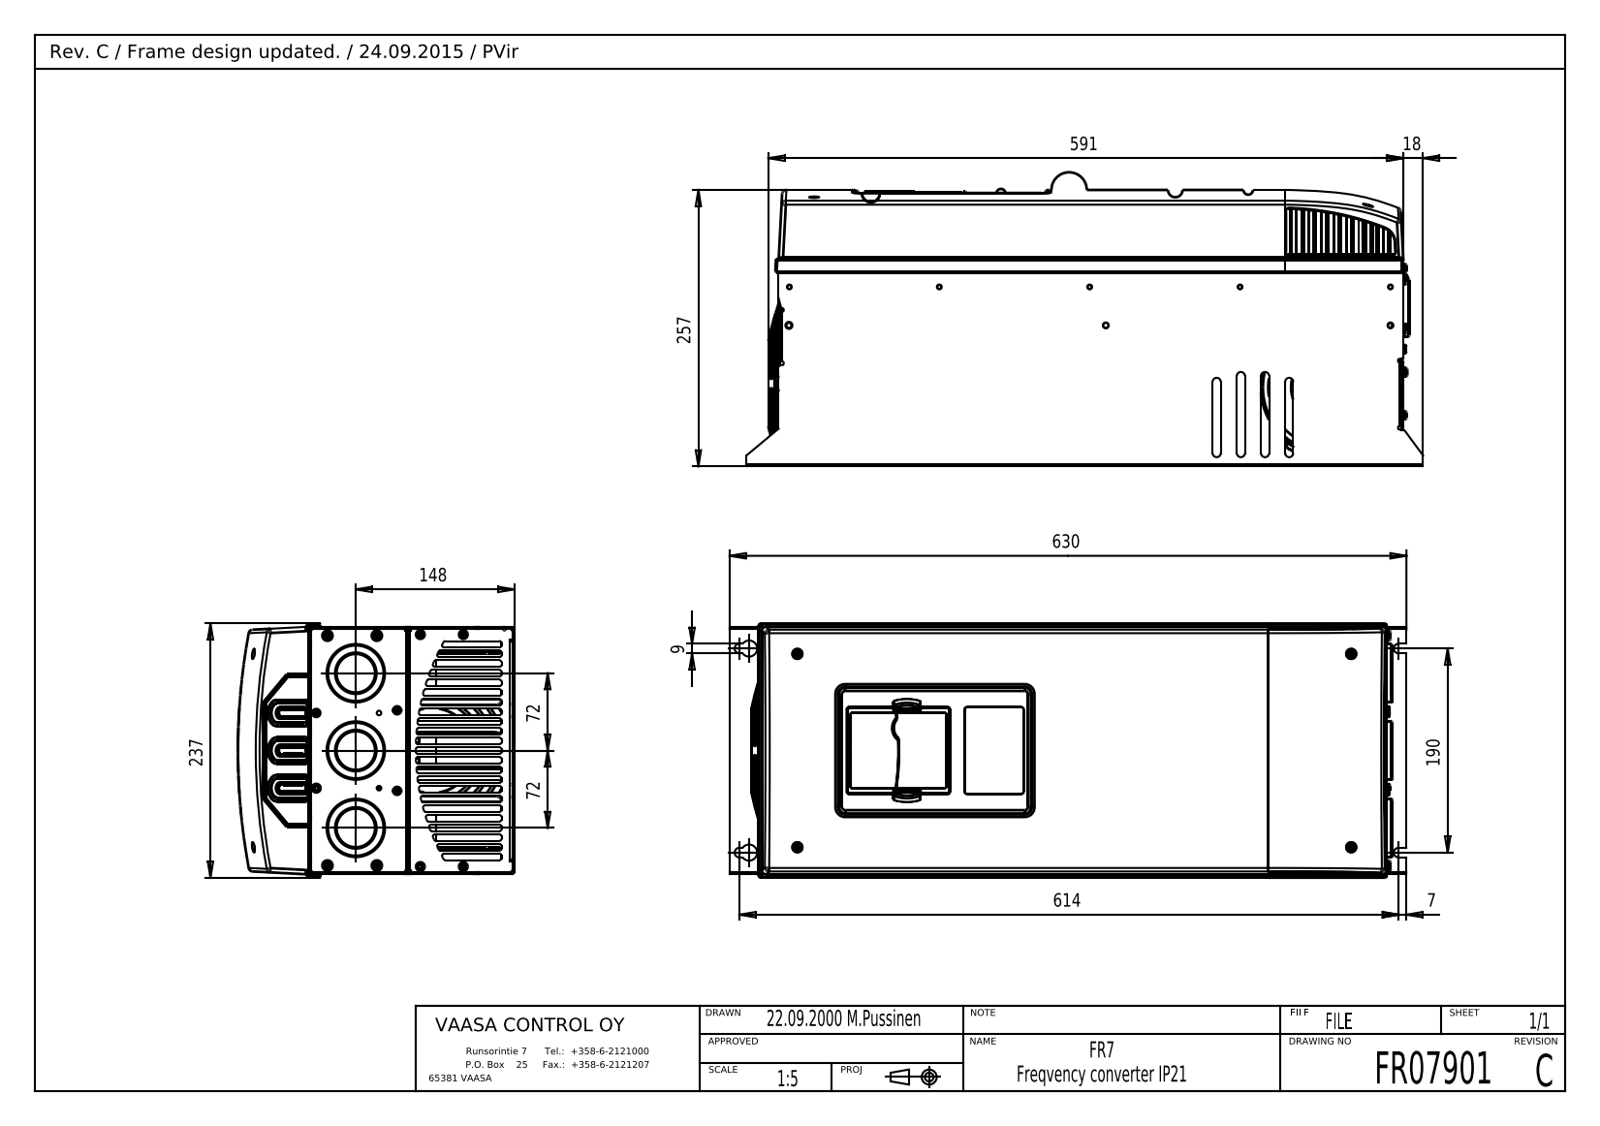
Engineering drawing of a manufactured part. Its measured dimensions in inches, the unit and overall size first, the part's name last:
Units: inches
Overall size (bounding box): 24.803 × 10.13 × 9.321
Round holes (diameter × count): ⌀0.13 ×8, ⌀0.177 ×4, ⌀0.197 ×4, ⌀0.354 ×4, ⌀0.591 ×2, ⌀1.496 ×2, ⌀0.118 ×1, ⌀0.142 ×1, ⌀1.417 ×1, ⌀4.362 ×1, ⌀5.094 ×1, ⌀5.827 ×1
Round bosses / shafts (diameter × count): ⌀0.315 ×8, ⌀0.354 ×7, ⌀0.394 ×6, ⌀2.126 ×2, ⌀0.169 ×2, ⌀5.331 ×1, ⌀4.598 ×1, ⌀3.866 ×1
Partial cylindrical surfaces — rounded edges, fillets, slot ends (radius × count): R0.079 ×94, R0.124 ×36, R0.02 ×16, R0.039 ×14, R0.008 ×10, R0.059 ×8, R0.148 ×8, R0.394 ×8
Main face-to-face distances: 0.059, 9.055, 7.48, 7.539, 0.118, 22.394, 7.421, 2.081, 2.022, 5.4
Hole centre spacings: 0.787, 1.438, 1.785, 2.197, 2.756, 3.97, 4.729, 7.087
Volume: 1 945 in³ · Surface area: 2 992 in²
Bodies: 1 solid, 1406 faces (616 planar, 480 cylindrical, 310 other)
Part name (STEP PRODUCT): VACON_FR7_IP21
STEP written by: CREO PARAMETRIC BY PTC INC, 2018070 (CONFIG_CONTROL_DESIGN)
